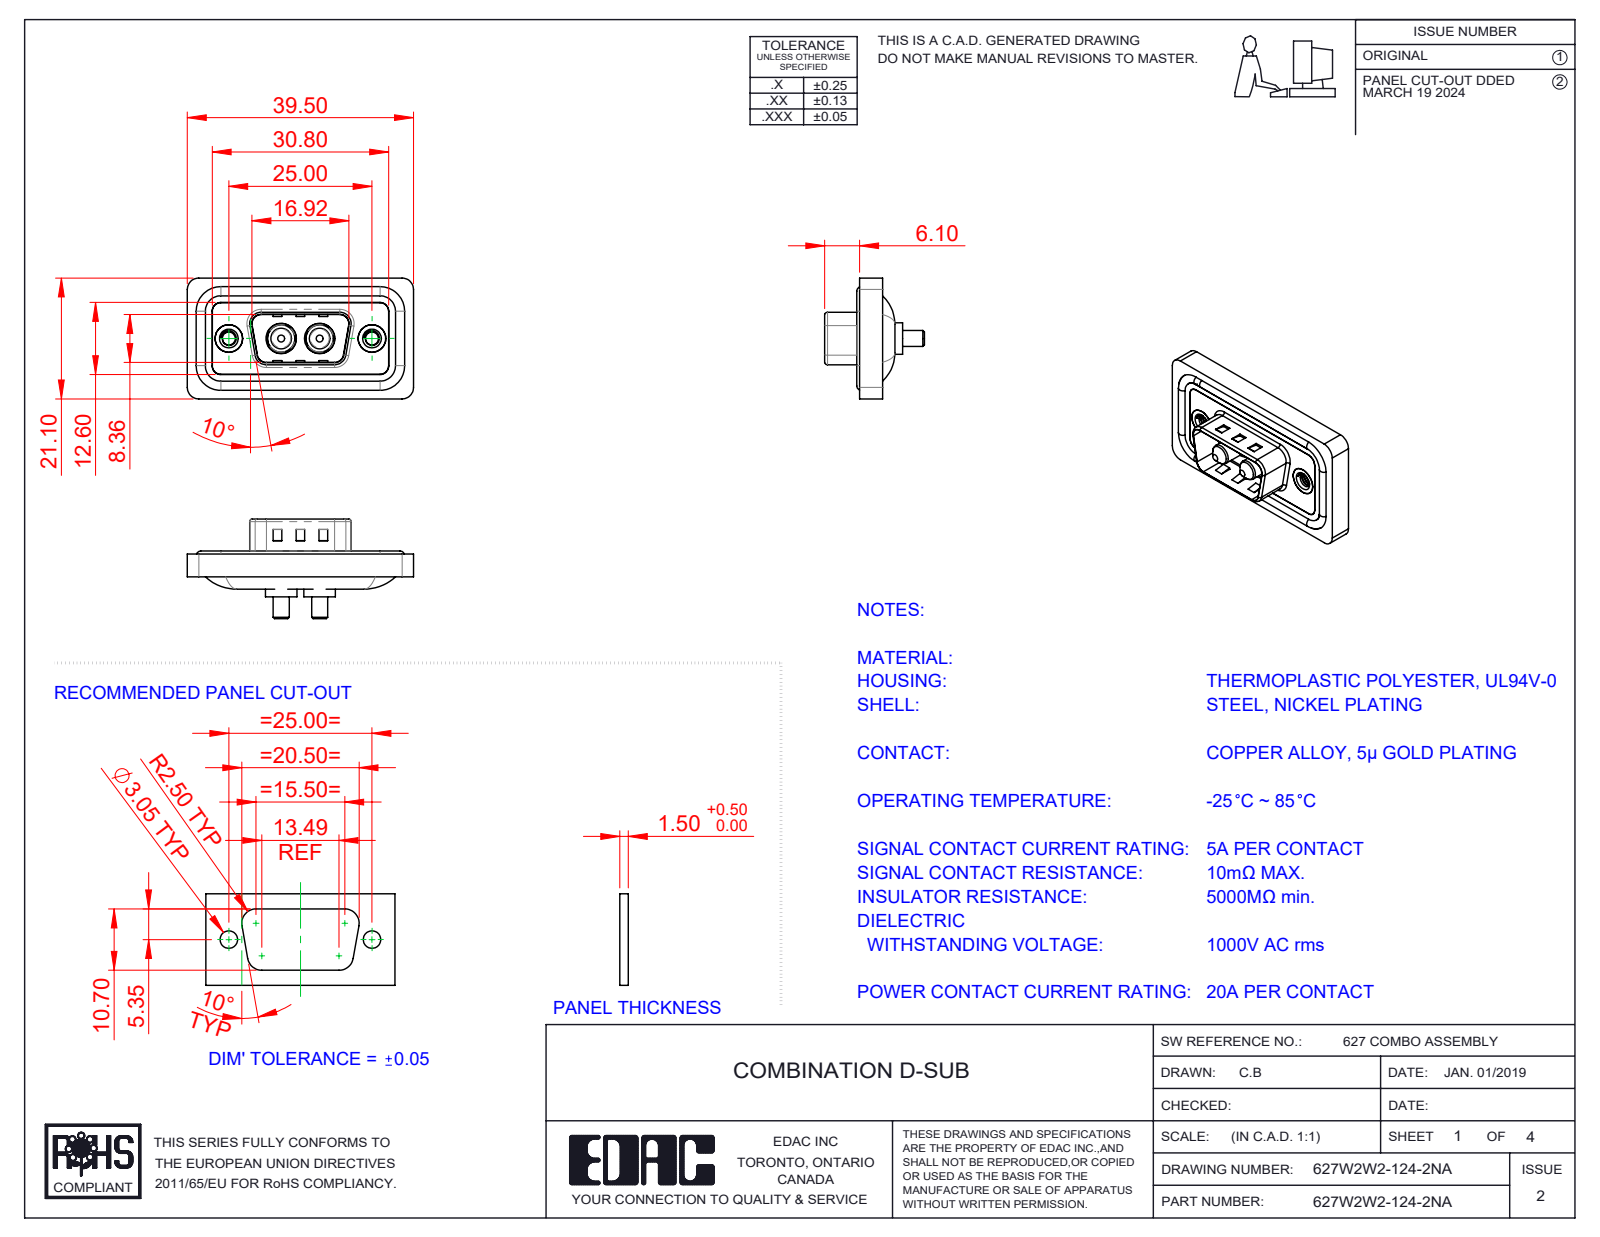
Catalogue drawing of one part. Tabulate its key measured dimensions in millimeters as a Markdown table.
| quantity | value |
| --- | --- |
| part name | 627Combo Waterproof Housing_09 Contacts; 627Combo Housing_2W2; Power Pin_20A S; 627Combo Shell Rear_09 Contacts (+3 more) |
| STEP written by | SolidWorks 2023 (CONFIG_CONTROL_DESIGN) |
| units | millimeters |
| bodies | 11 solids, 487 faces (165 planar, 220 cylindrical, 102 other) |
| overall size | 39.5 × 21.1 × 17.4 |
| volume | 4 462 mm³ |
| surface area | 6 981 mm² |
| round holes (diameter × count) | 2.26 × 2, 4 × 2, 4.8 × 2, 4.85 × 2, 5 × 2, 5.3 × 2 |
| round bosses / shafts (diameter × count) | 1.6 × 4, 5.5 × 2, 5.2 × 2, 4.9 × 2, 4.75 × 2, 3.75 × 2, 3.6 × 2, 2.8 × 2 |
| partial cylindrical surfaces (radius × count) | 1.5 × 22, 2 × 18, 0.5 × 8, 1.6 × 8, 0.25 × 4, 0.6 × 4, 0.65 × 4, 0.9 × 4 |
| main face-to-face distances | 0.4, 1.1, 2.9, 3.1, 0.5, 1.6, 1.5, 4, 2.5, 0.7 |
| hole center spacings | 9.14, 15.86, 6.72, 25 |
